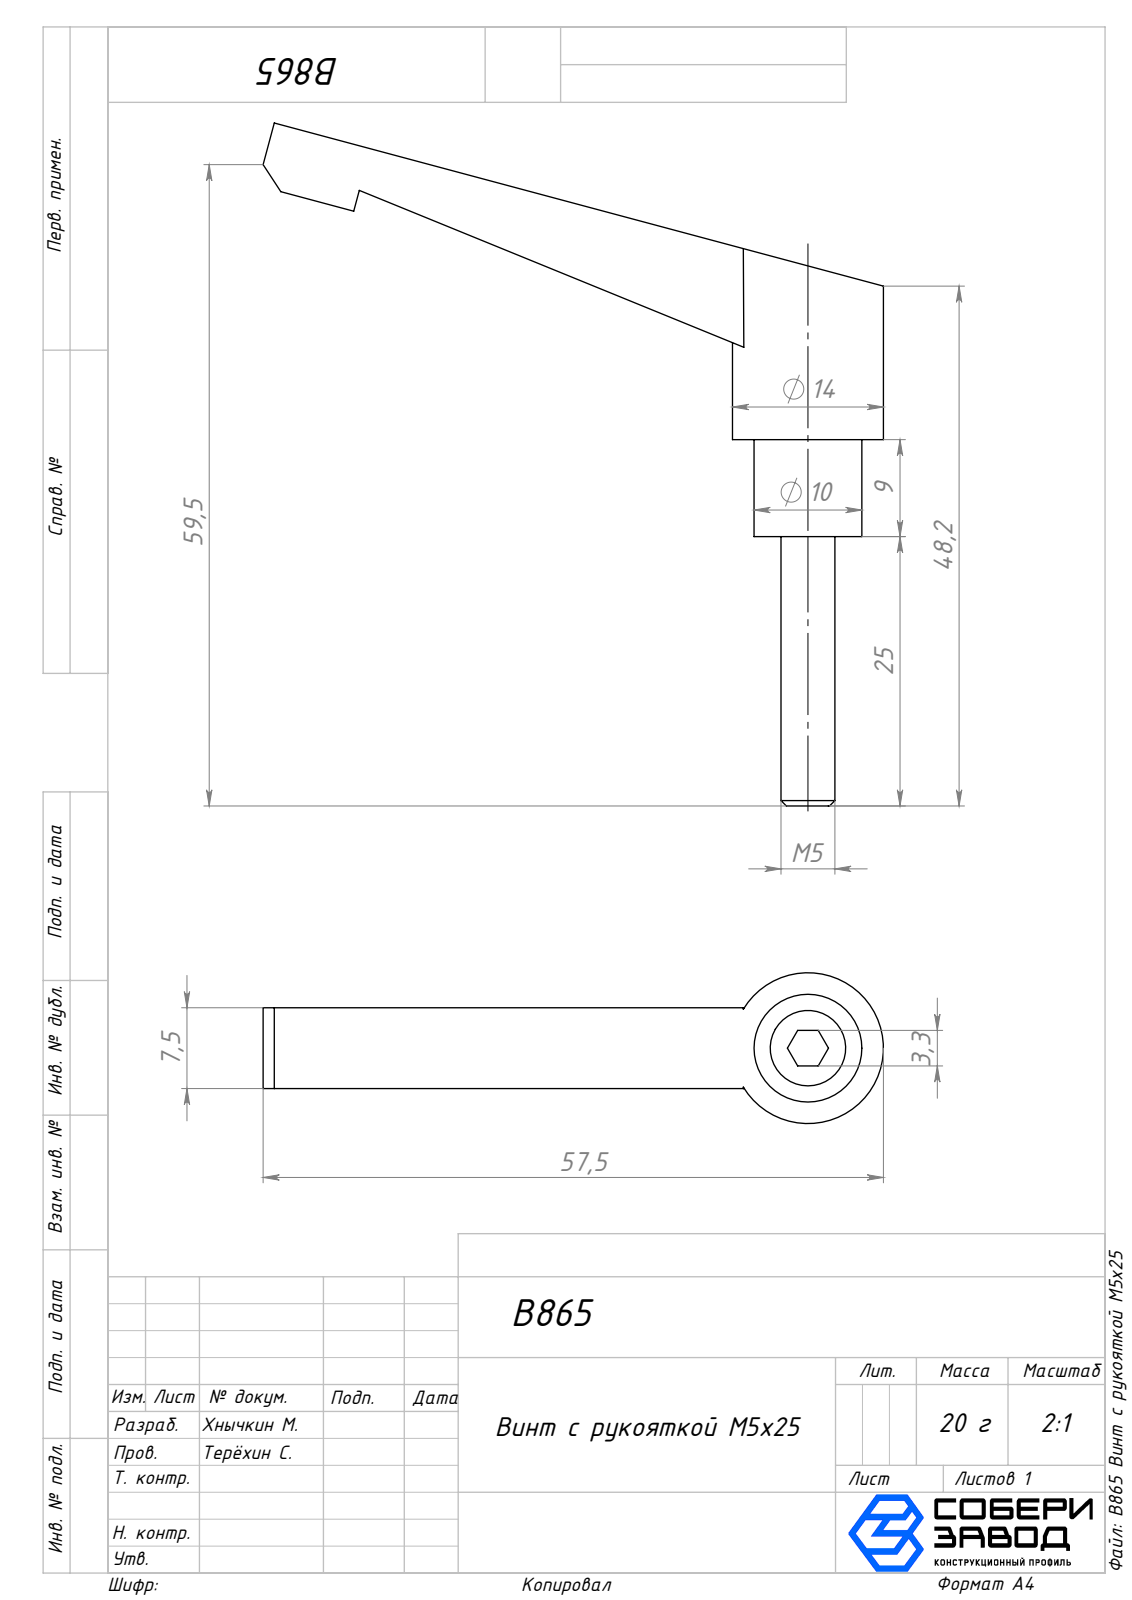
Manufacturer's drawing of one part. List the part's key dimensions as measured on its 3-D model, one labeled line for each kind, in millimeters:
Part name (STEP PRODUCT): Рукоятка_00; B865 Винт с рукояткой М5х25; Винтик_00; Винт с рукояткой_00
STEP written by: SolidWorks 2025 (AUTOMOTIVE_DESIGN)
Units: millimetres
Bodies: 3 solids, 52 faces (32 planar, 18 cylindrical, 2 other)
Overall size (bounding box): 63.39 × 57.54 × 14
Volume: 4 787 mm³ · Surface area: 4 511 mm²
Round holes (diameter × count): ⌀3 ×1, ⌀6 ×1, ⌀10 ×1
Round bosses / shafts (diameter × count): ⌀14 ×1, ⌀7 ×1, ⌀5 ×1
Main face-to-face distances: 1, 7.5, 6.5, 5.5, 3.5, 10, 11, 9, 19, 20
